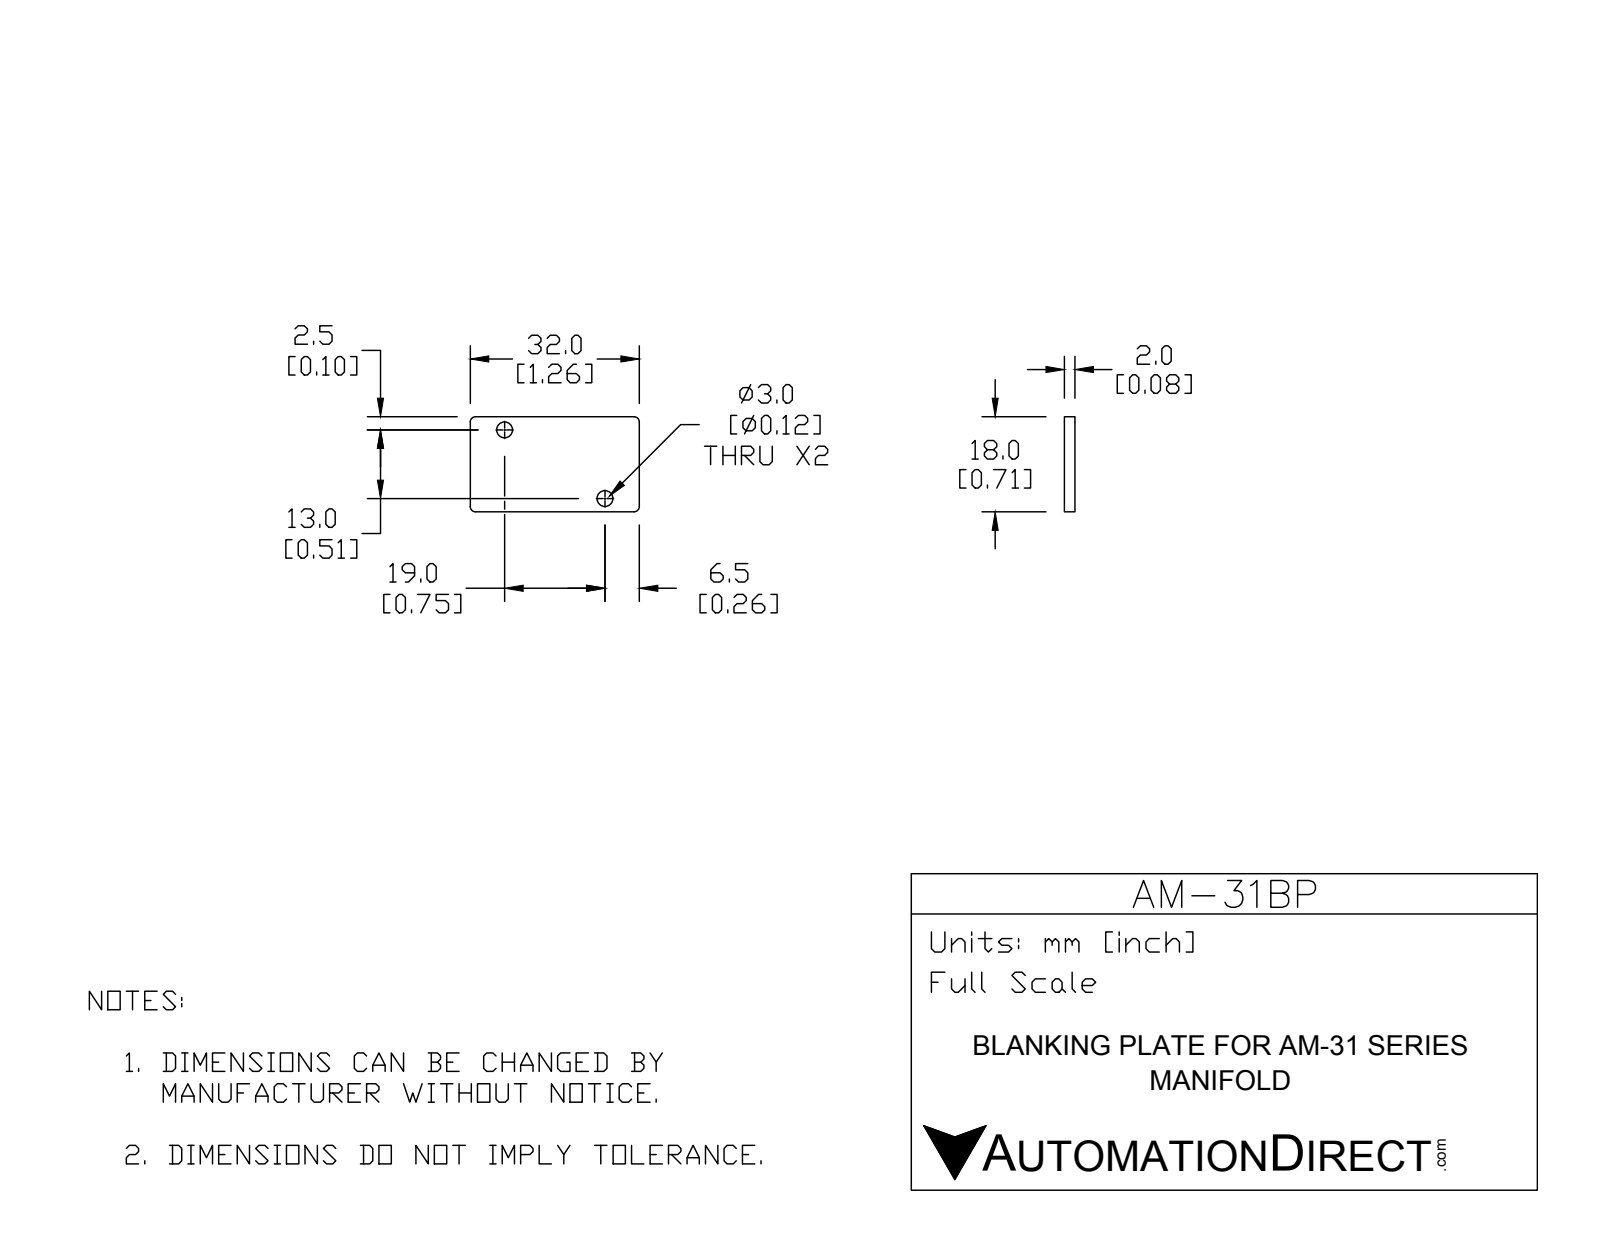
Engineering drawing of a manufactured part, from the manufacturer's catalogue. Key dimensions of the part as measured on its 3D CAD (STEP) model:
Part name (STEP PRODUCT): AM-31BP
STEP written by: SolidWorks 2016 (AUTOMOTIVE_DESIGN)
Units: millimetres
Bodies: 1 solid, 14 faces (6 planar, 8 cylindrical, 0 other)
Overall size (bounding box): 32 × 18 × 2
Volume: 1 122 mm³ · Surface area: 1 356 mm²
Round holes (diameter × count): ⌀3 ×2
Partial cylindrical surfaces — rounded edges, fillets, slot ends (radius × count): R1 ×4
Main face-to-face distances: 2, 18, 32
Hole centre spacings: 23.02
